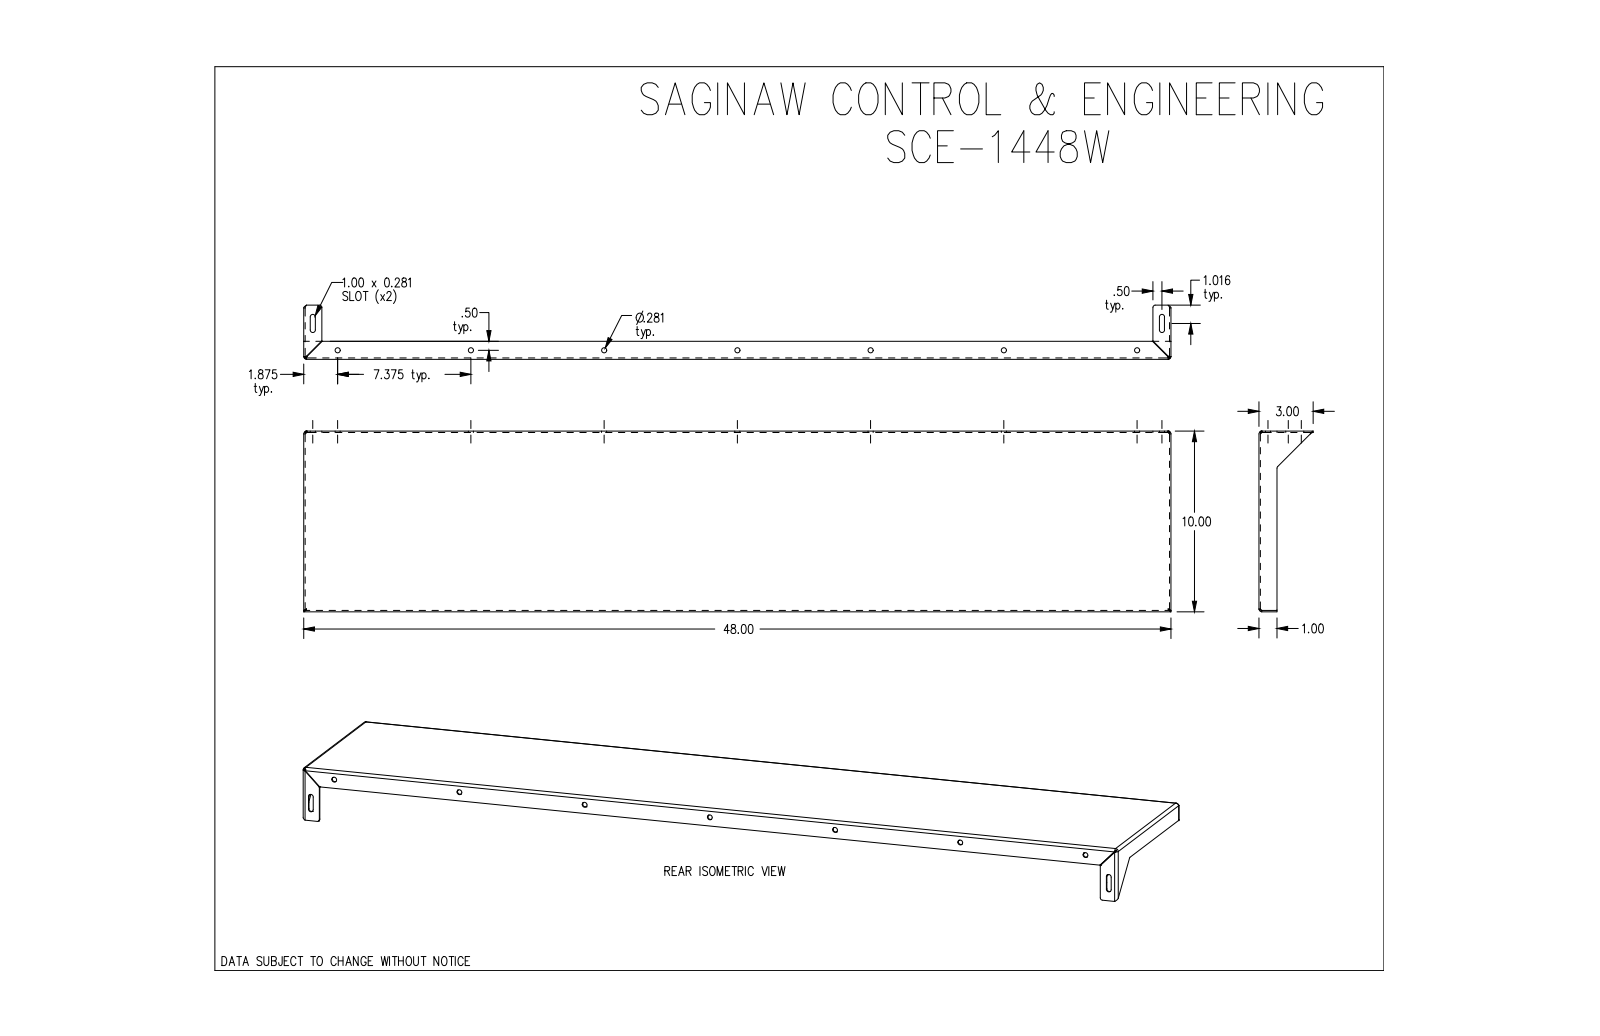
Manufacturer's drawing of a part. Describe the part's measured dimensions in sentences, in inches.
The part is named "SCE-1448W". Its 3-D file was written by "SolidWorks 2019 (AUTOMOTIVE_DESIGN)". It is 1 solid with 47 faces: 28 planar, 17 cylindrical and 2 other. Overall it measures 48 by 10 by 3 inches. Its volume is 29.61 cubic inches and its surface area 1 191 square inches. Round holes: 7 of diameter 0.281. Partial cylindrical surfaces (rounded edges, fillets, slot ends): 4 of radius 0.141, 2 of radius 0.106, 2 of radius 0.156, 1 of radius 0.125. The main face-to-face distances are 0.05, 9.95, 10, 9.9, 47.95, 48, 47.9, 0.95, 1, 9.94. The hole center spacings are 14.75, 7.375, 7.375, 29.5, 22.125, 22.125, 36.875, 36.875.
